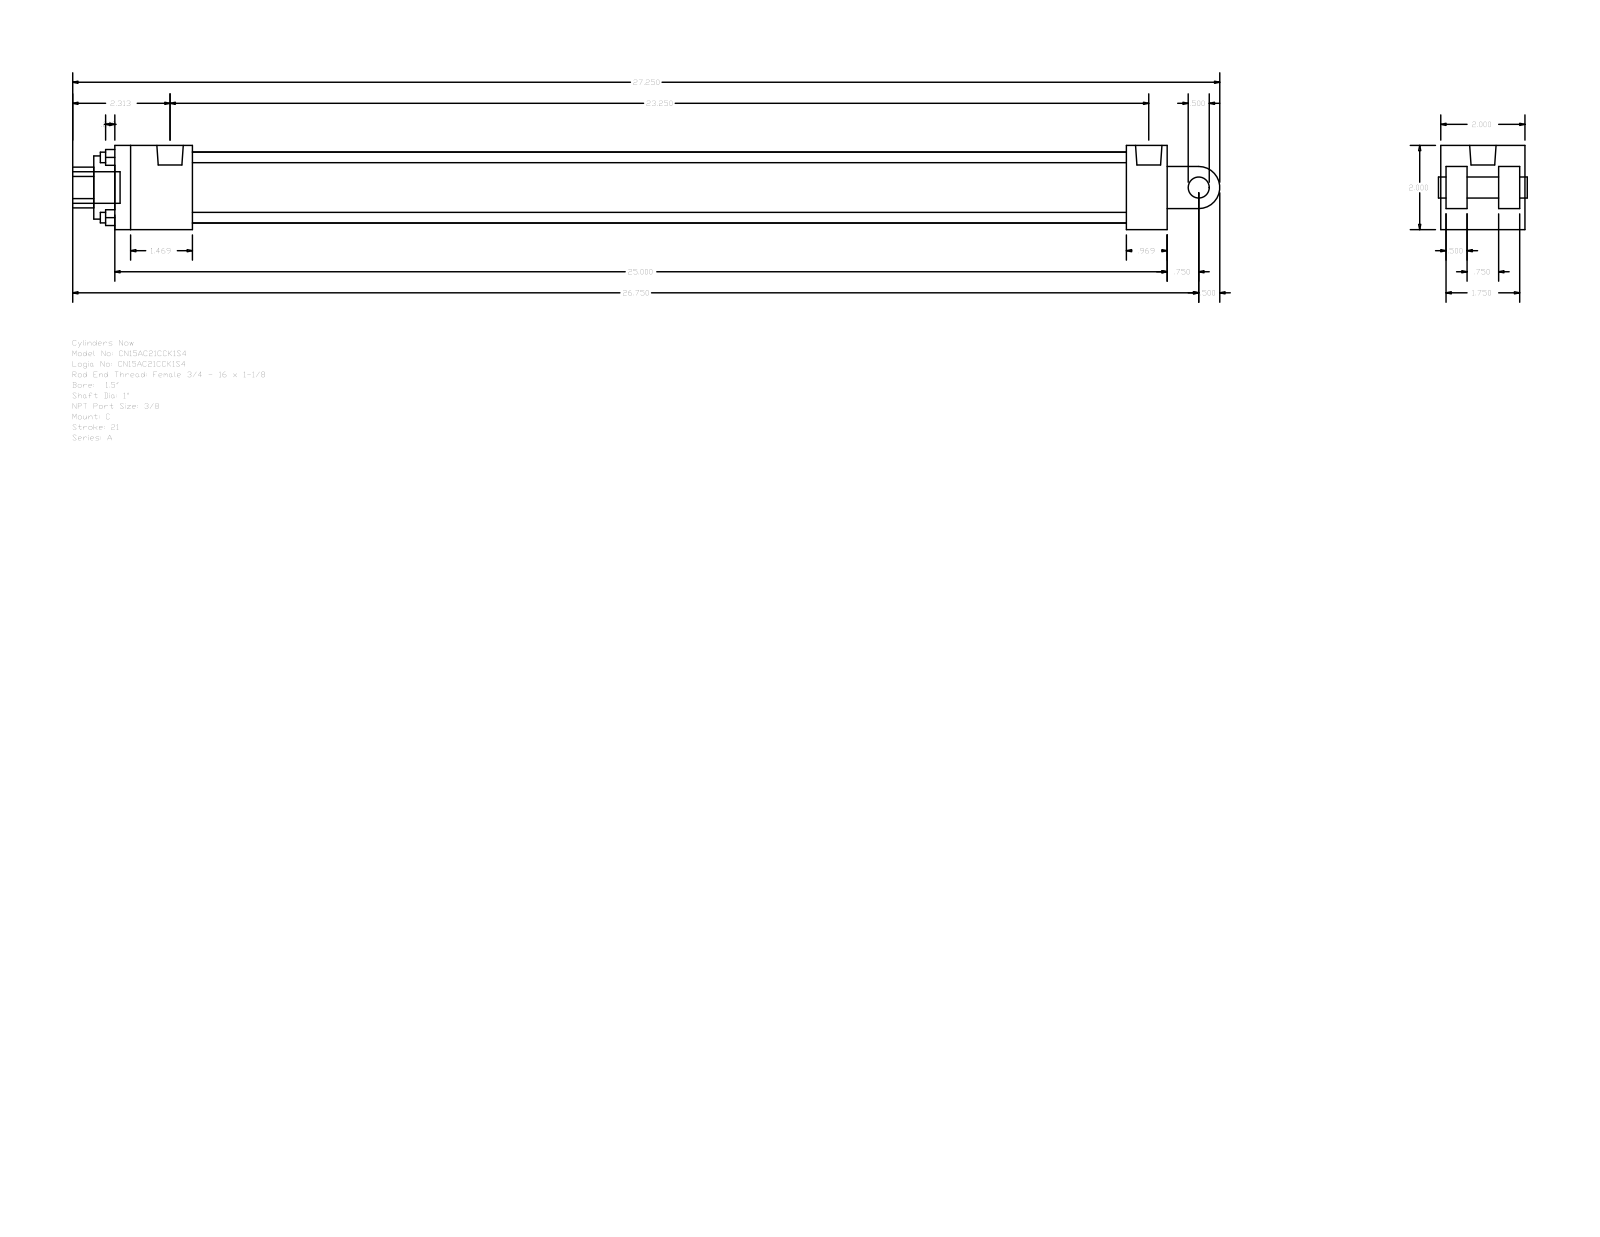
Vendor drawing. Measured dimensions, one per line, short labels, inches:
name: A_C__0150_1
written by: GSSL Pune (CONFIG_CONTROL_DESIGN)
unit: in
bodies: 0 solids, 99 faces (70 planar, 29 cylindrical, 0 other)
size: 27.25 × 2 × 2
holes: 4× ⌀0.25, 2× ⌀0.219, 1× ⌀0.627, 1× ⌀1, 1× ⌀1.5, 1× ⌀1.69
bosses: 2× ⌀0.219, 1× ⌀0.75, 1× ⌀0.627, 1× ⌀0.5
rounds: 1× R0.484, 1× R0.5
face distances: 2, 0.5, 0.125, 0.625, 1.875, 1.375, 1.25, 25, 24.031, 0.969
hole spacings: 1.011, 1.43, 2.022, 0.156
